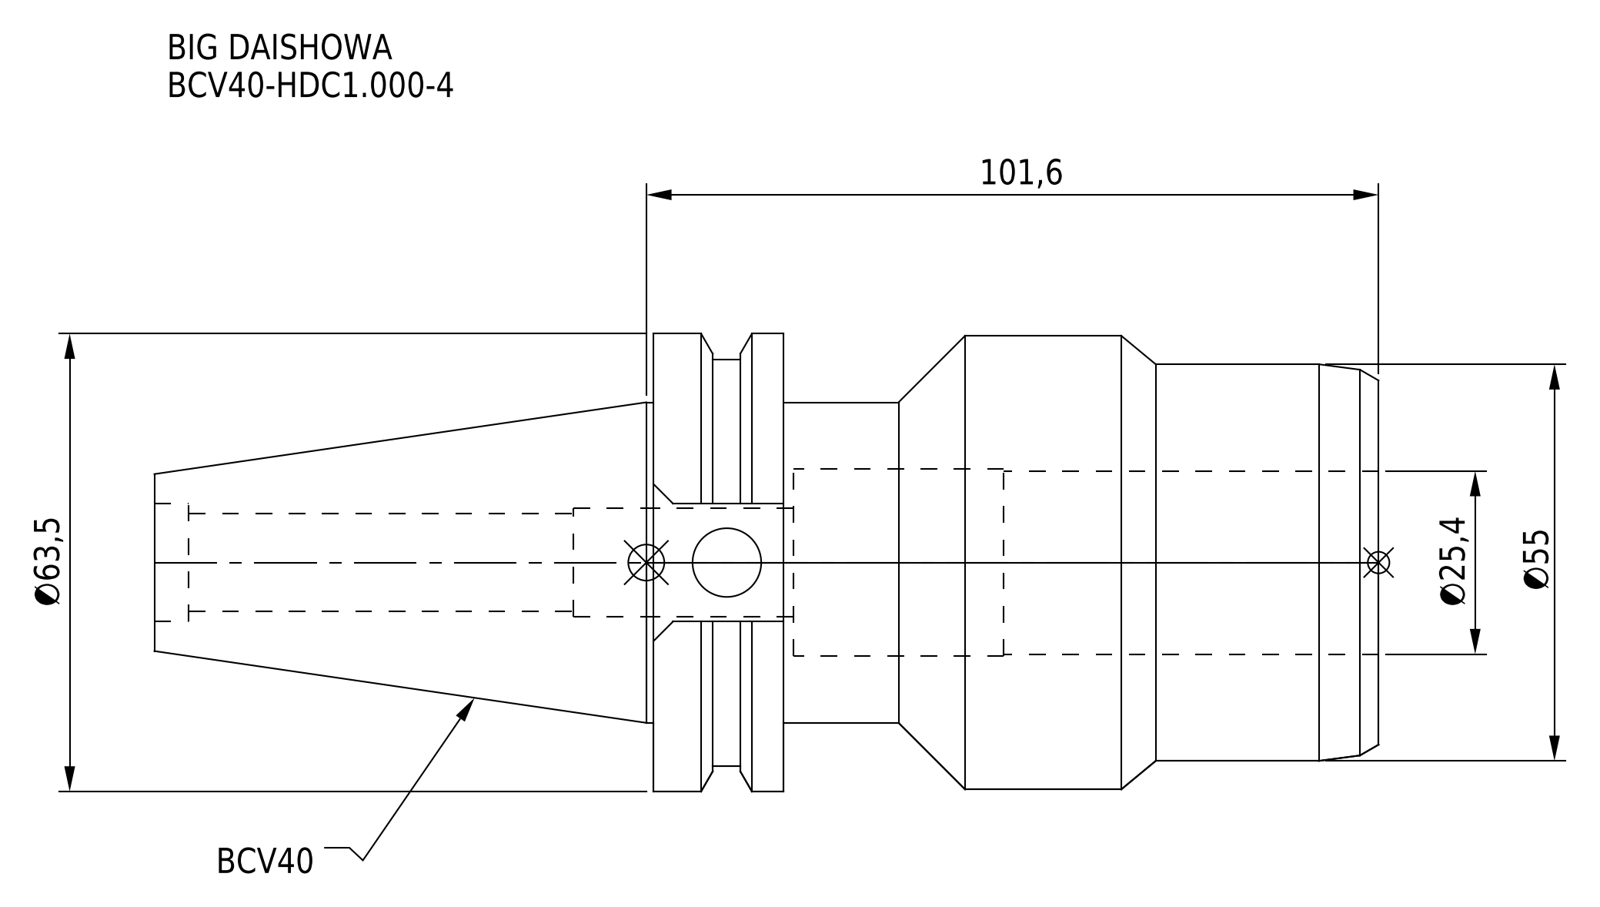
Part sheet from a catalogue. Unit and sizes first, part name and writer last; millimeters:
Units: millimetres
Overall size (bounding box): 169.85 × 63.5 × 62.9
Round holes (diameter × count): ⌀9.53 ×1, ⌀13.6 ×1, ⌀15 ×1, ⌀16.32 ×1, ⌀25.4 ×1, ⌀25.9 ×1
Round bosses / shafts (diameter × count): ⌀63.5 ×1, ⌀62.9 ×1, ⌀56.36 ×1, ⌀55 ×1, ⌀44.45 ×1
Main face-to-face distances: 82.55, 100.6, 18.05, 81.2, 1.35, 19.4, 169.85, 88.65, 87.3, 69.25
Volume: 259 615 mm³ · Surface area: 42 901 mm²
Bodies: 1 solid, 65 faces (23 planar, 28 cylindrical, 14 other)
Part name (STEP PRODUCT): BCV40-HDC1_000-4
STEP written by: CREO PARAMETRIC BY PTC INC, 2016380 (AUTOMOTIVE_DESIGN)
